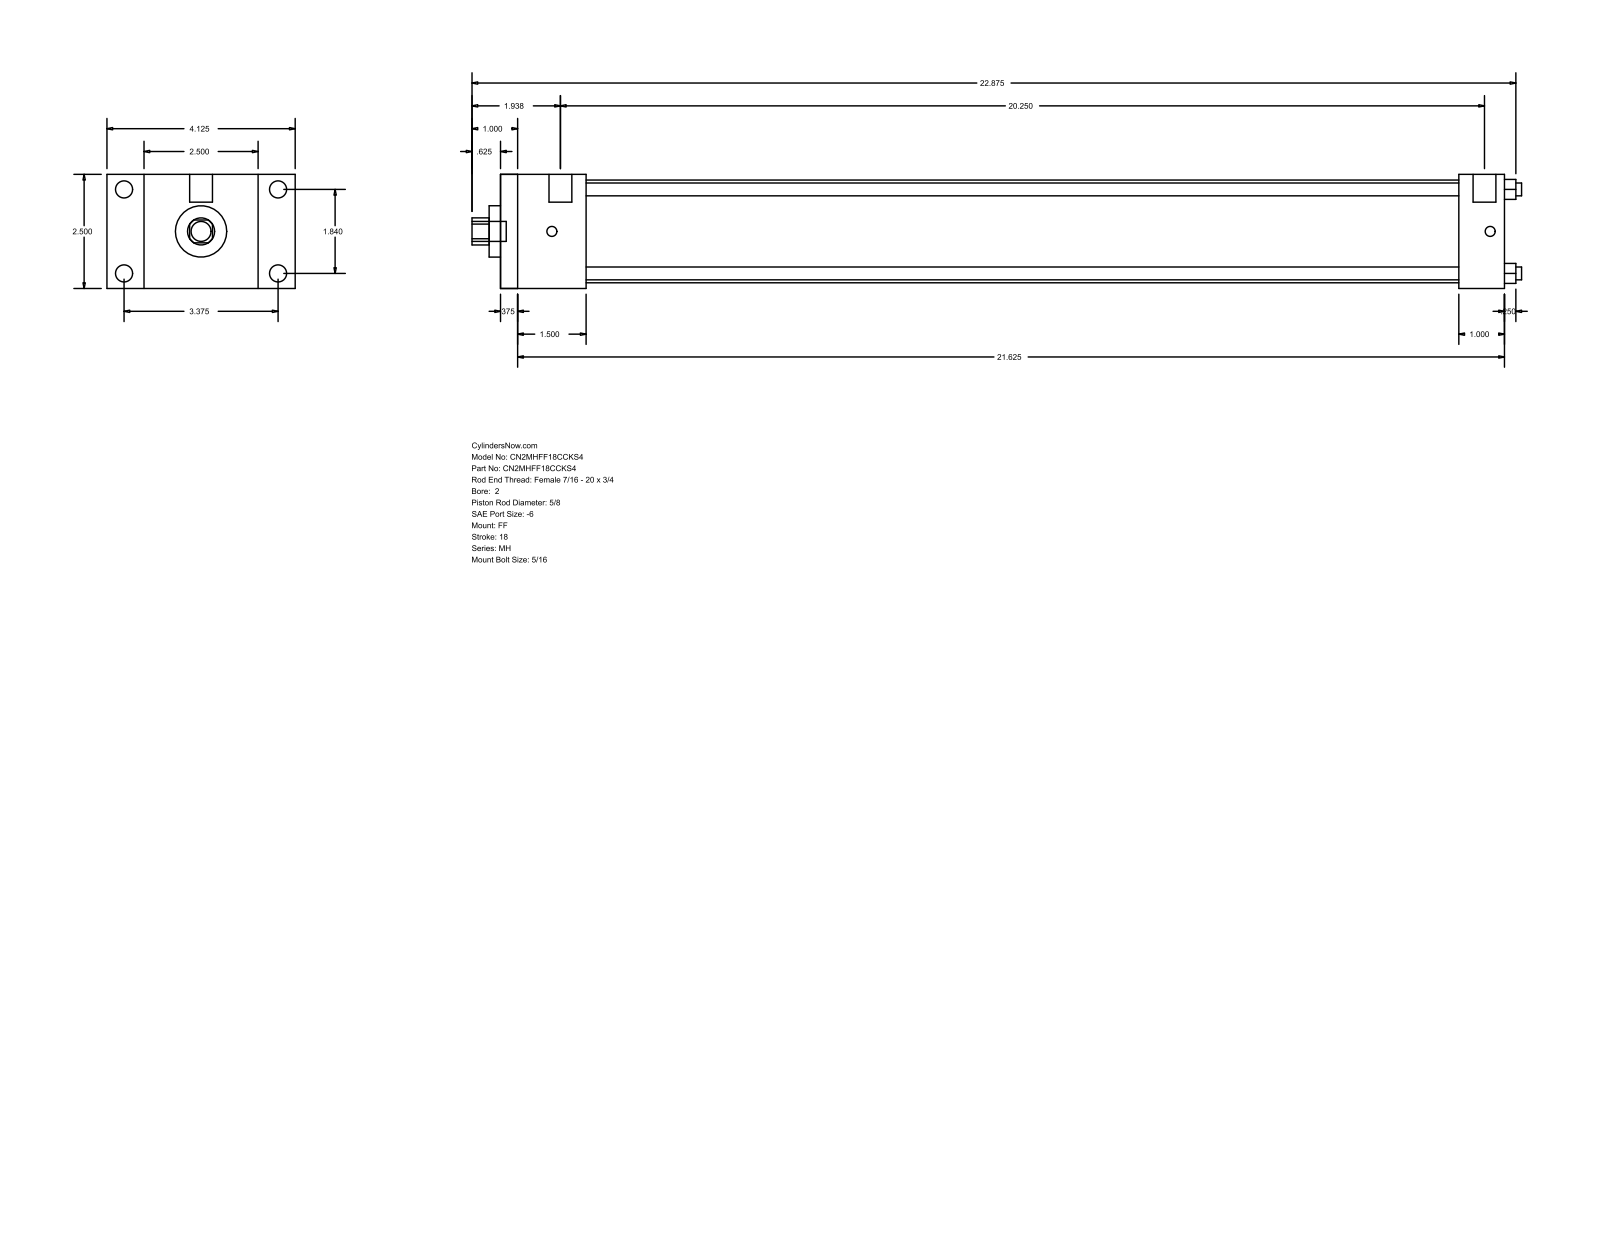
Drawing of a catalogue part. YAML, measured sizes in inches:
part_name: "MH_FF__0200_0.625"
step_written_by: "GSSL Pune (CONFIG_CONTROL_DESIGN)"
units: inches
bodies: {solids: 0, faces: 92, planar: 64, cylindrical: 28, other: 0}
overall_size: [23, 4.125, 2.5]
round_holes:
  - {diameter: 0.281, count: 4}
  - {diameter: 0.625, count: 1}
  - {diameter: 1.125, count: 1}
  - {diameter: 2.25, count: 1}
round_bosses_or_shafts:
  - {diameter: 0.375, count: 4}
  - {diameter: 0.219, count: 4}
  - {diameter: 0.5, count: 2}
  - {diameter: 0.437, count: 1}
partial_cylinders:
  - {radius: 0.297, count: 1}
face_to_face_distances: [2.5, 22, 0.375, 21.625, 1, 1.5, 1.875, 21, 20.625, 19.125]
hole_center_spacings: [1.301, 1.84, 2.602]
